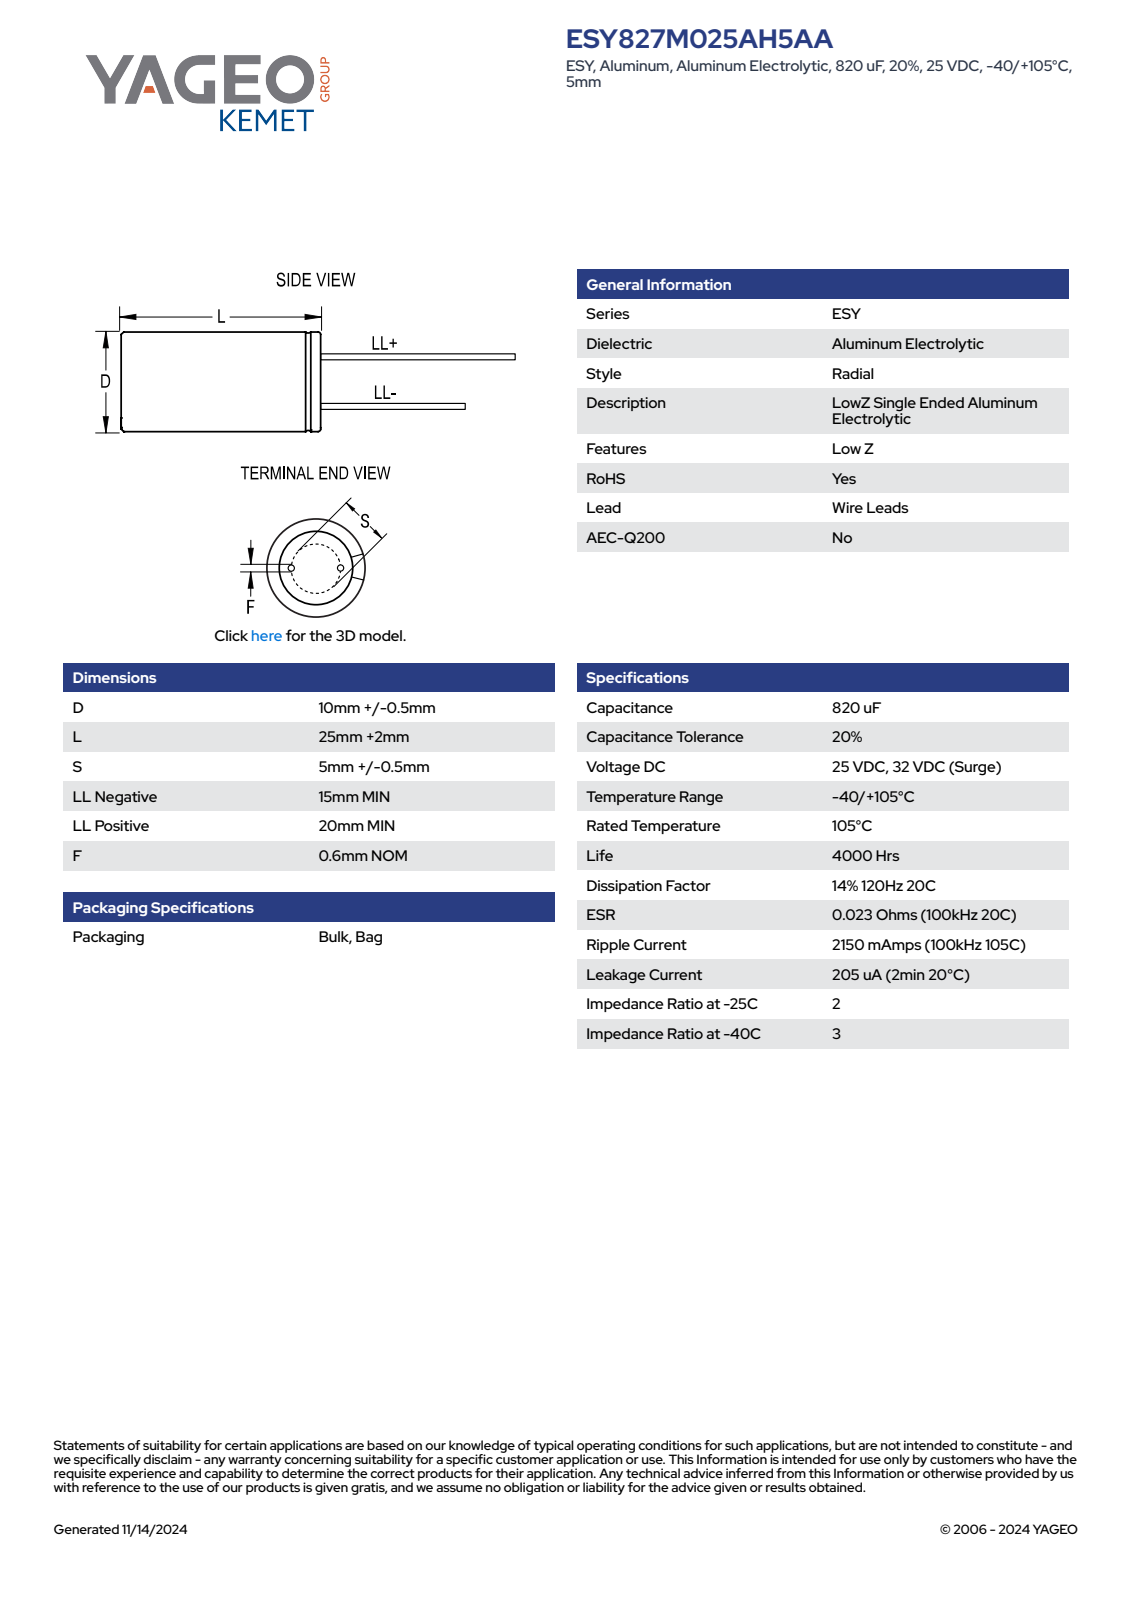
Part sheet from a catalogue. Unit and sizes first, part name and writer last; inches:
Units: inches
Overall size (bounding box): 1.851 × 0.413 × 0.413
Round bosses / shafts (diameter × count): ⌀0.024 ×2, ⌀0.413 ×1
Main face-to-face distances: 1.063, 1.063, 1.654, 1.851, 1.654, 1.85, 0.591, 0.787, 0.197, 0.056
Volume: 0.143 in³ · Surface area: 1.789 in²
Bodies: 4 solids, 75 faces (61 planar, 8 cylindrical, 6 other)
Part name (STEP PRODUCT): CAR_KLP_10X25_D10.5L27S5F0.6
STEP written by: SolidWorks 2014 (AUTOMOTIVE_DESIGN)
